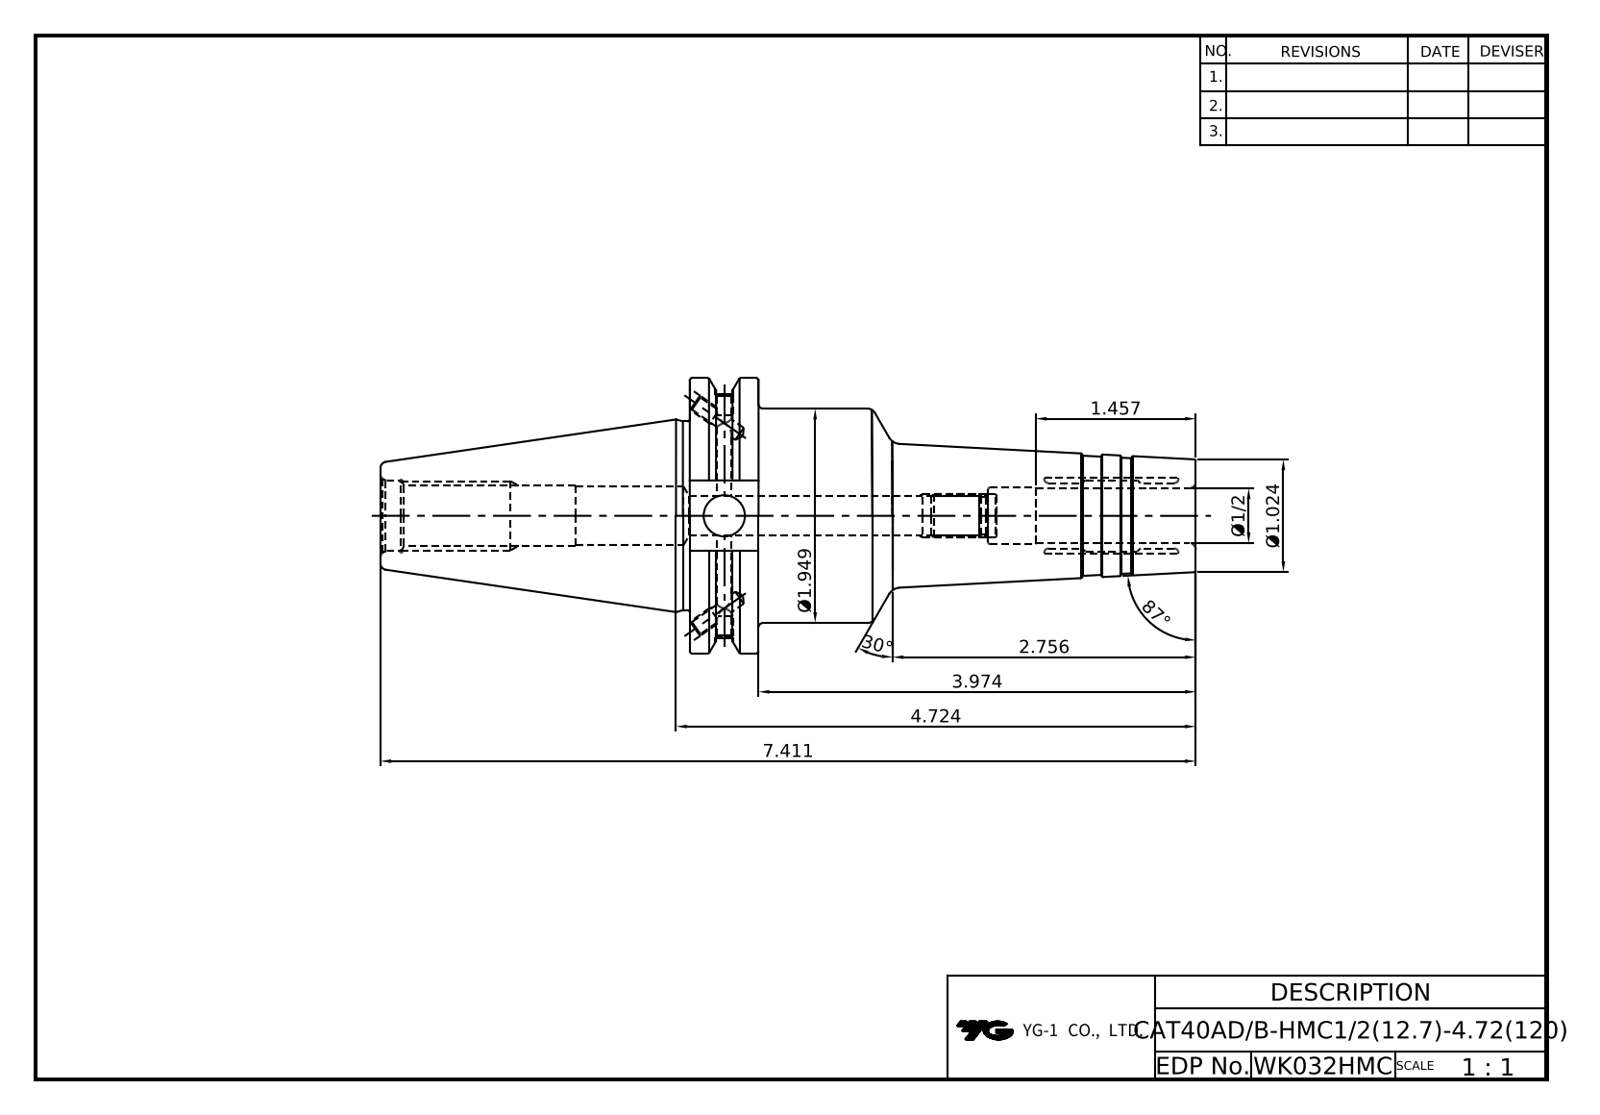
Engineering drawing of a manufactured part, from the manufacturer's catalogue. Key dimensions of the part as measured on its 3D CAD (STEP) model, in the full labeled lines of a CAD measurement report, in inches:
Part name (STEP PRODUCT): LO-CAT40ADB-HMC12.7-120
STEP written by: Autodesk Inventor 2020 (AUTOMOTIVE_DESIGN)
Units: inches
Bodies: 1 solid, 106 faces (36 planar, 30 cylindrical, 40 other)
Overall size (bounding box): 7.411 × 2.5 × 2.405
Volume: 12.06 in³ · Surface area: 53.39 in²
Round holes (diameter × count): ⌀0.128 ×4, ⌀0.157 ×2, ⌀0.165 ×2, ⌀0.351 ×1, ⌀0.375 ×1, ⌀0.5 ×1, ⌀0.512 ×1, ⌀0.52 ×1, ⌀0.527 ×1, ⌀0.642 ×1
Round bosses / shafts (diameter × count): ⌀2.5 ×1, ⌀1.949 ×1, ⌀1.717 ×1
Partial cylindrical surfaces — rounded edges, fillets, slot ends (radius × count): R0.322 ×1, R1.108 ×1
Main face-to-face distances: 0.625, 4.6, 3.974, 1.874, 0.645, 2.812, 3.437, 7.411, 3.05, 0.238
